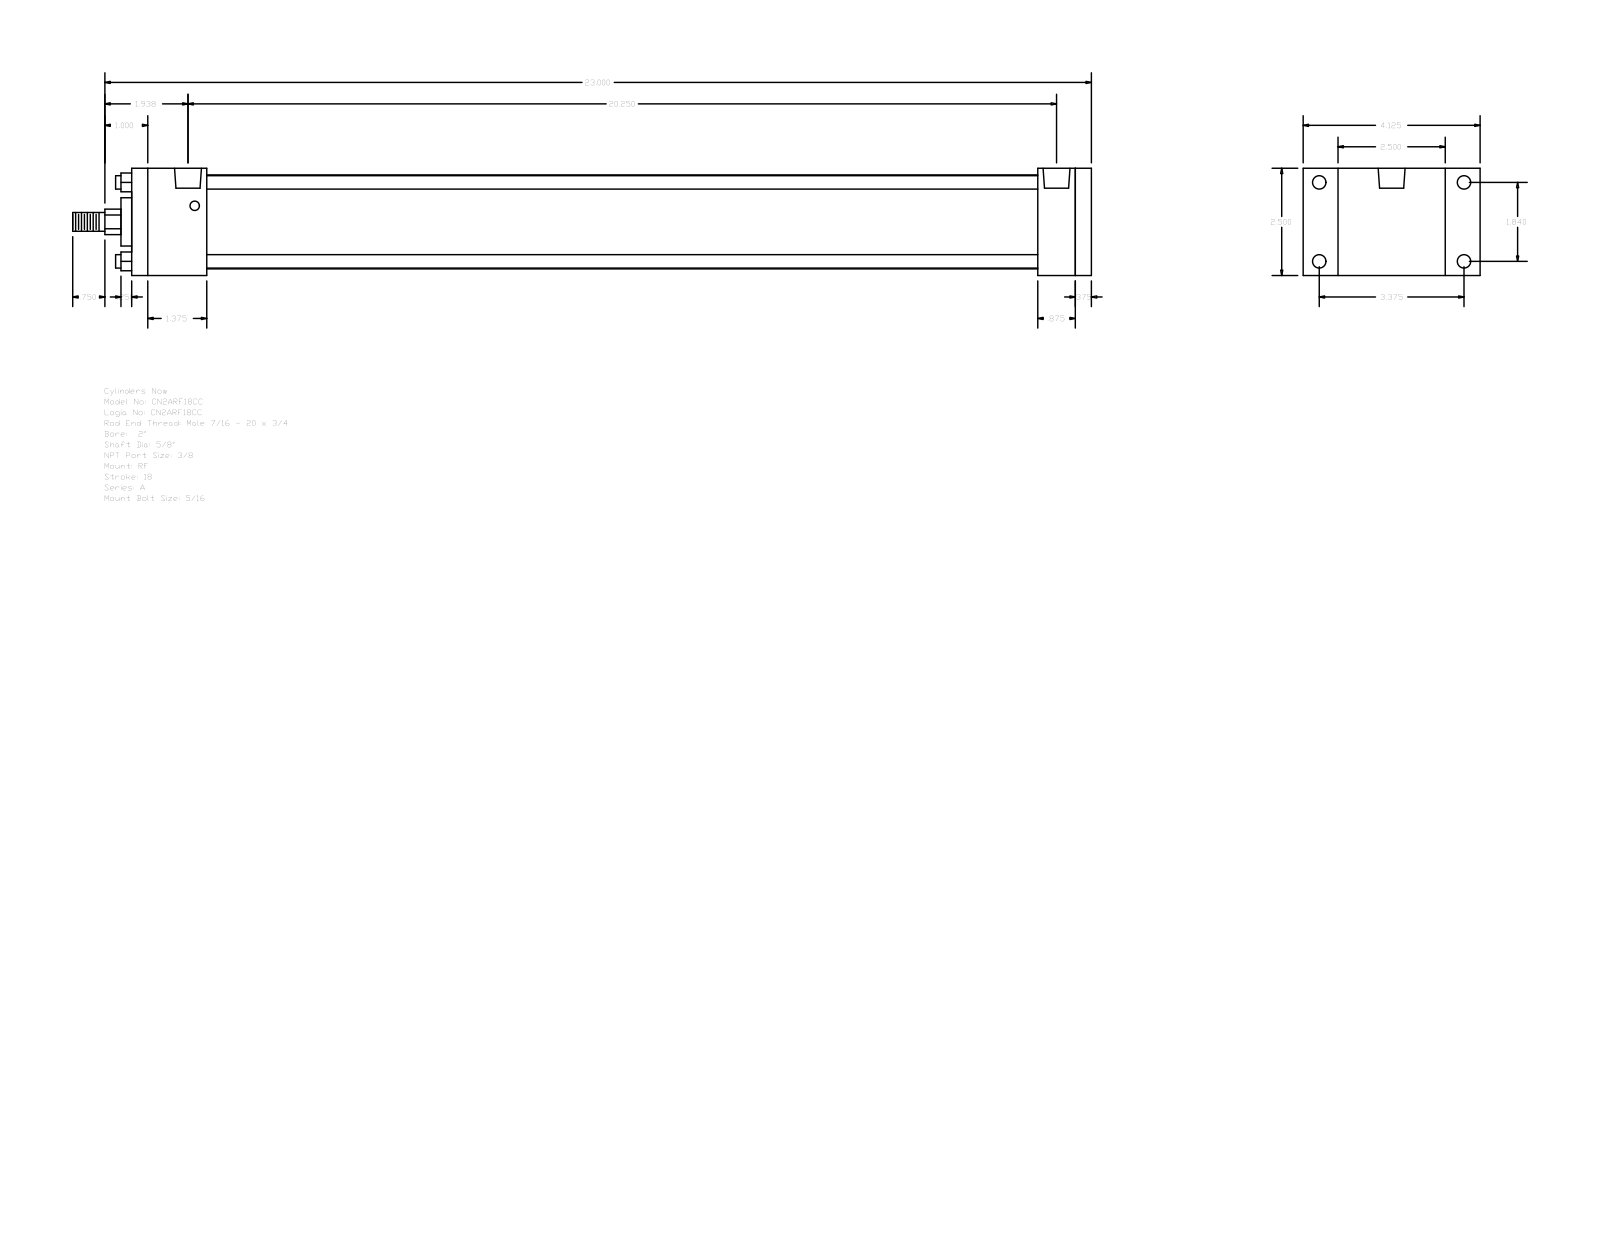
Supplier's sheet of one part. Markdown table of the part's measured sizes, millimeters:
| quantity | value |
| --- | --- |
| part name | A_RF__0200_0.625 |
| STEP written by | GSSL Pune (CONFIG_CONTROL_DESIGN) |
| units | millimeters |
| bodies | 0 solids, 92 faces (64 planar, 28 cylindrical, 0 other) |
| overall size | 603.25 × 104.78 × 63.5 |
| round holes (diameter × count) | 5.56 × 4, 7.94 × 4, 15.93 × 2 |
| round bosses / shafts (diameter × count) | 7.94 × 4, 55.63 × 1, 28.57 × 1, 15.88 × 1, 11.11 × 1 |
| partial cylindrical surfaces (radius × count) | 7.54 × 1 |
| main face-to-face distances | 63.5, 568.32, 9.53, 558.79, 44.45, 514.34, 523.87, 536.57, 492.12, 22.22 |
| hole center spacings | 46.74, 85.72, 97.63, 506.4, 3.97, 3.98, 510.37, 510.38 |
